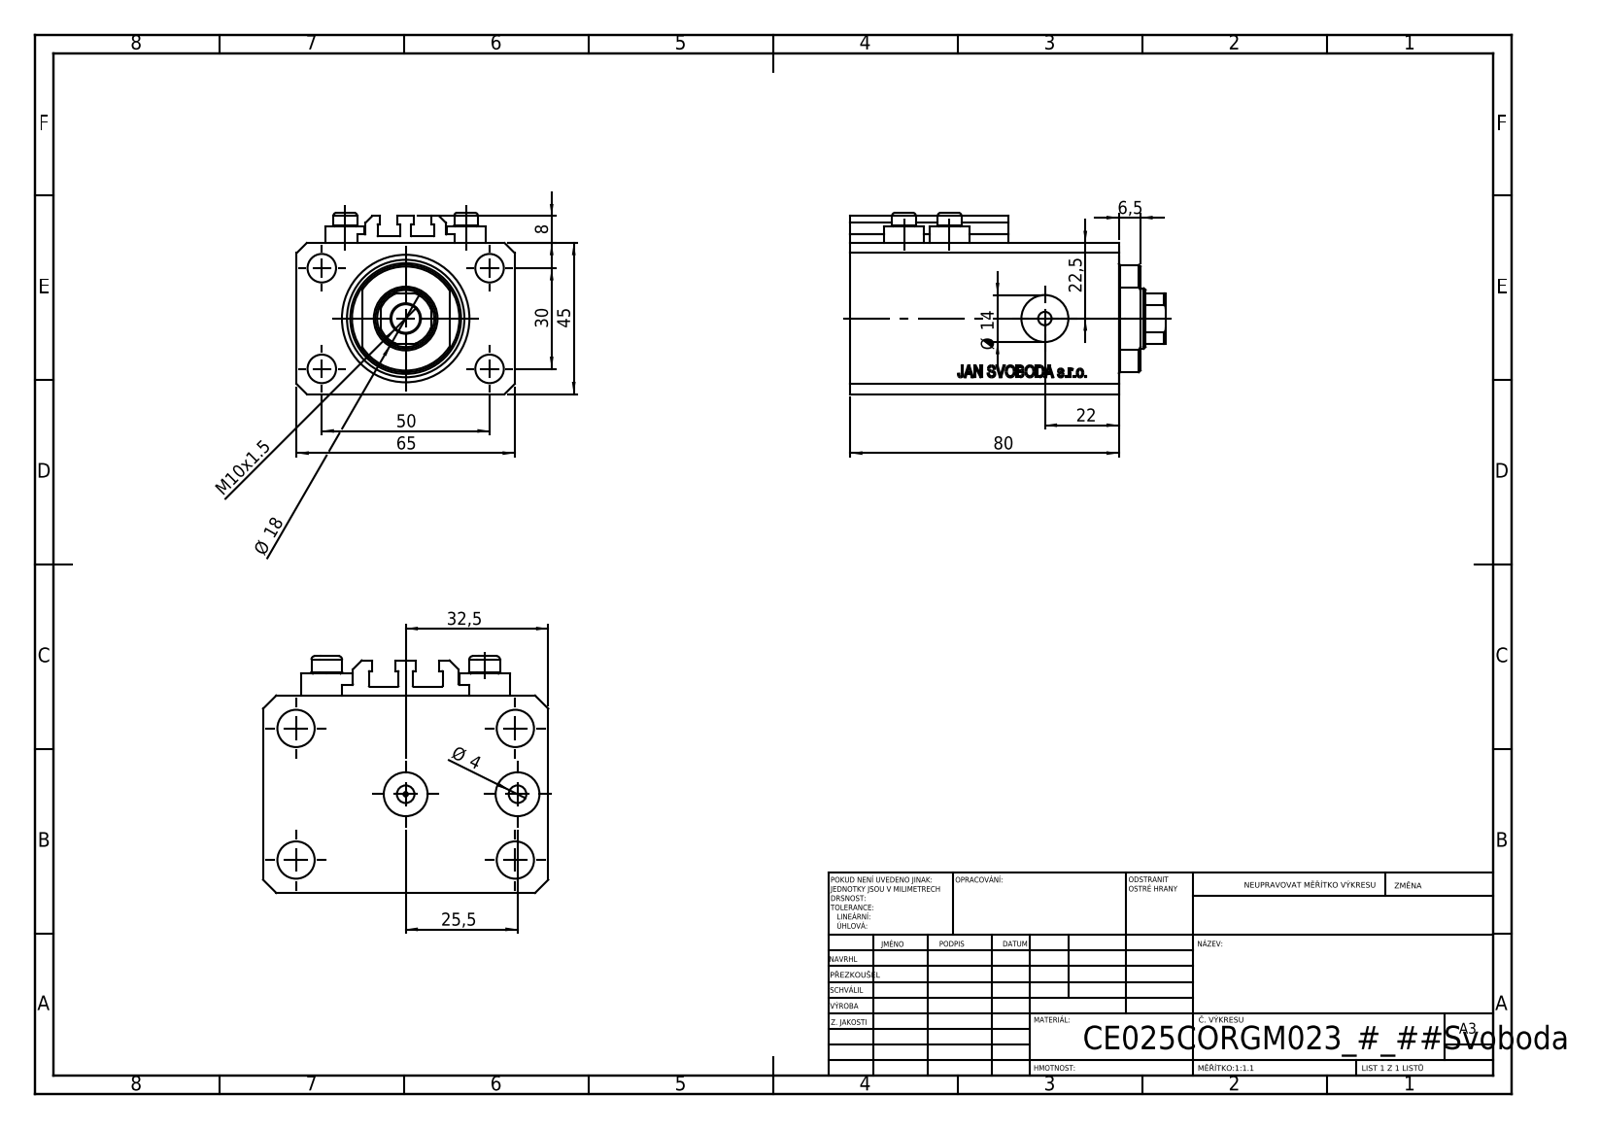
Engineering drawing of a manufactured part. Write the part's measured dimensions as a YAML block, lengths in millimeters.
part_name: "V250CE_VC_C; V250CE_C_VCP; V250CE_C_Body; ALLEN BOLT V250CE"
step_written_by: "SolidWorks 2019 (CONFIG_CONTROL_DESIGN)"
units: millimeters
bodies: {solids: 8, faces: 1042, planar: 504, cylindrical: 92, other: 446}
overall_size: [94, 65, 54]
volume: 219210
surface_area: 59347
round_holes:
  - {diameter: 4, count: 8}
  - {diameter: 8.5, count: 5}
  - {diameter: 10, count: 2}
  - {diameter: 14, count: 2}
  - {diameter: 1.25, count: 1}
  - {diameter: 18, count: 1}
  - {diameter: 25, count: 1}
  - {diameter: 38, count: 1}
round_bosses_or_shafts:
  - {diameter: 11.6, count: 4}
  - {diameter: 7, count: 4}
partial_cylinders:
  - {radius: 0.2, count: 10}
  - {radius: 8.5, count: 1}
  - {radius: 16, count: 1}
face_to_face_distances: [45, 65, 14, 80, 66, 47, 6.9, 59.1, 73.1, 3]
hole_center_spacings: [29.15, 36, 13.6, 15.01, 30, 38.48, 50, 52.68]
